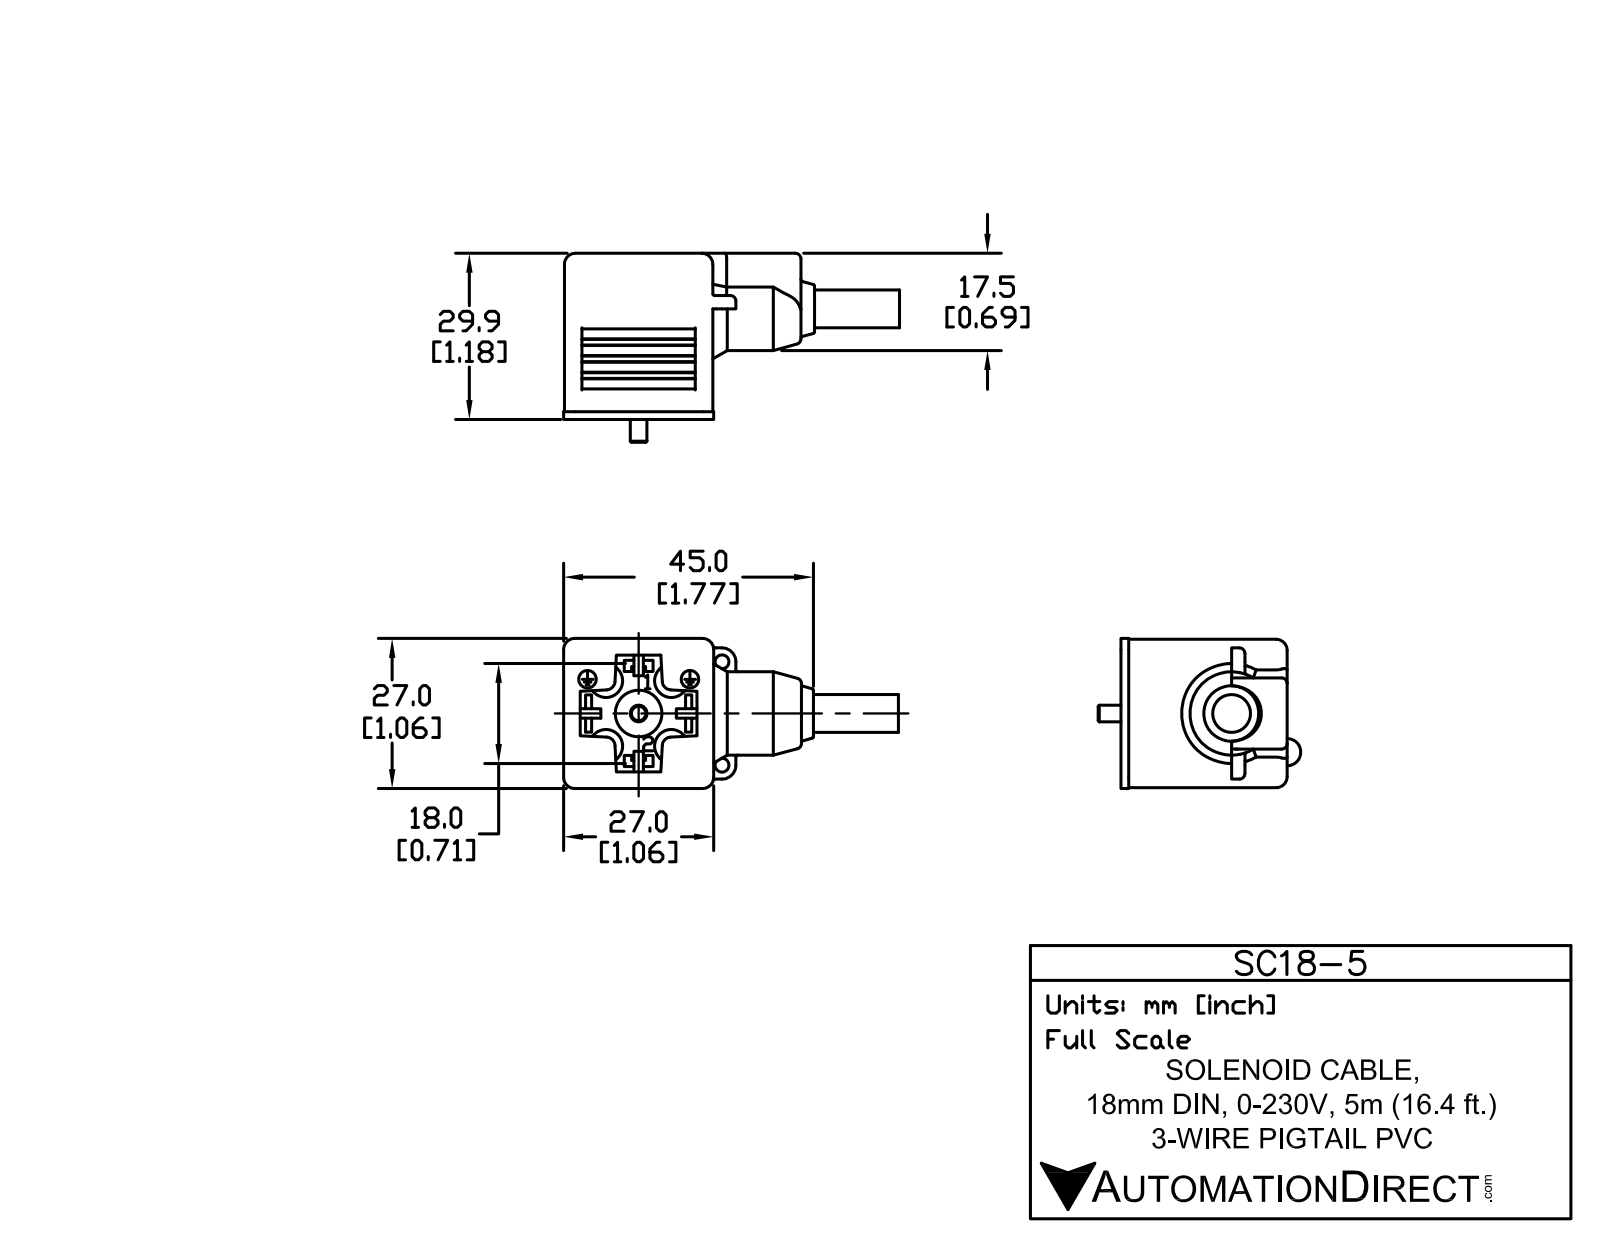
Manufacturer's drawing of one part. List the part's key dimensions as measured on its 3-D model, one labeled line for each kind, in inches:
Part name (STEP PRODUCT): SC18-5
STEP written by: SolidWorks 2011 (AUTOMOTIVE_DESIGN)
Units: inches
Bodies: 4 solids, 266 faces (209 planar, 33 cylindrical, 24 other)
Overall size (bounding box): 2.884 × 1.323 × 1.063
Volume: 1.36 in³ · Surface area: 12.75 in²
Round holes (diameter × count): ⌀0.089 ×2, ⌀0.236 ×2, ⌀0.157 ×1, ⌀0.331 ×1
Round bosses / shafts (diameter × count): ⌀0.226 ×1, ⌀0.108 ×1
Partial cylindrical surfaces — rounded edges, fillets, slot ends (radius × count): R0.039 ×11, R0.079 ×4, R0.118 ×4, R0.295 ×1
Main face-to-face distances: 1.063, 0.915, 0.079, 0.994, 0.039, 0.876, 0.954, 1.051, 0.787, 0.276
Hole centre spacings: 0.231, 0.232, 0.463
